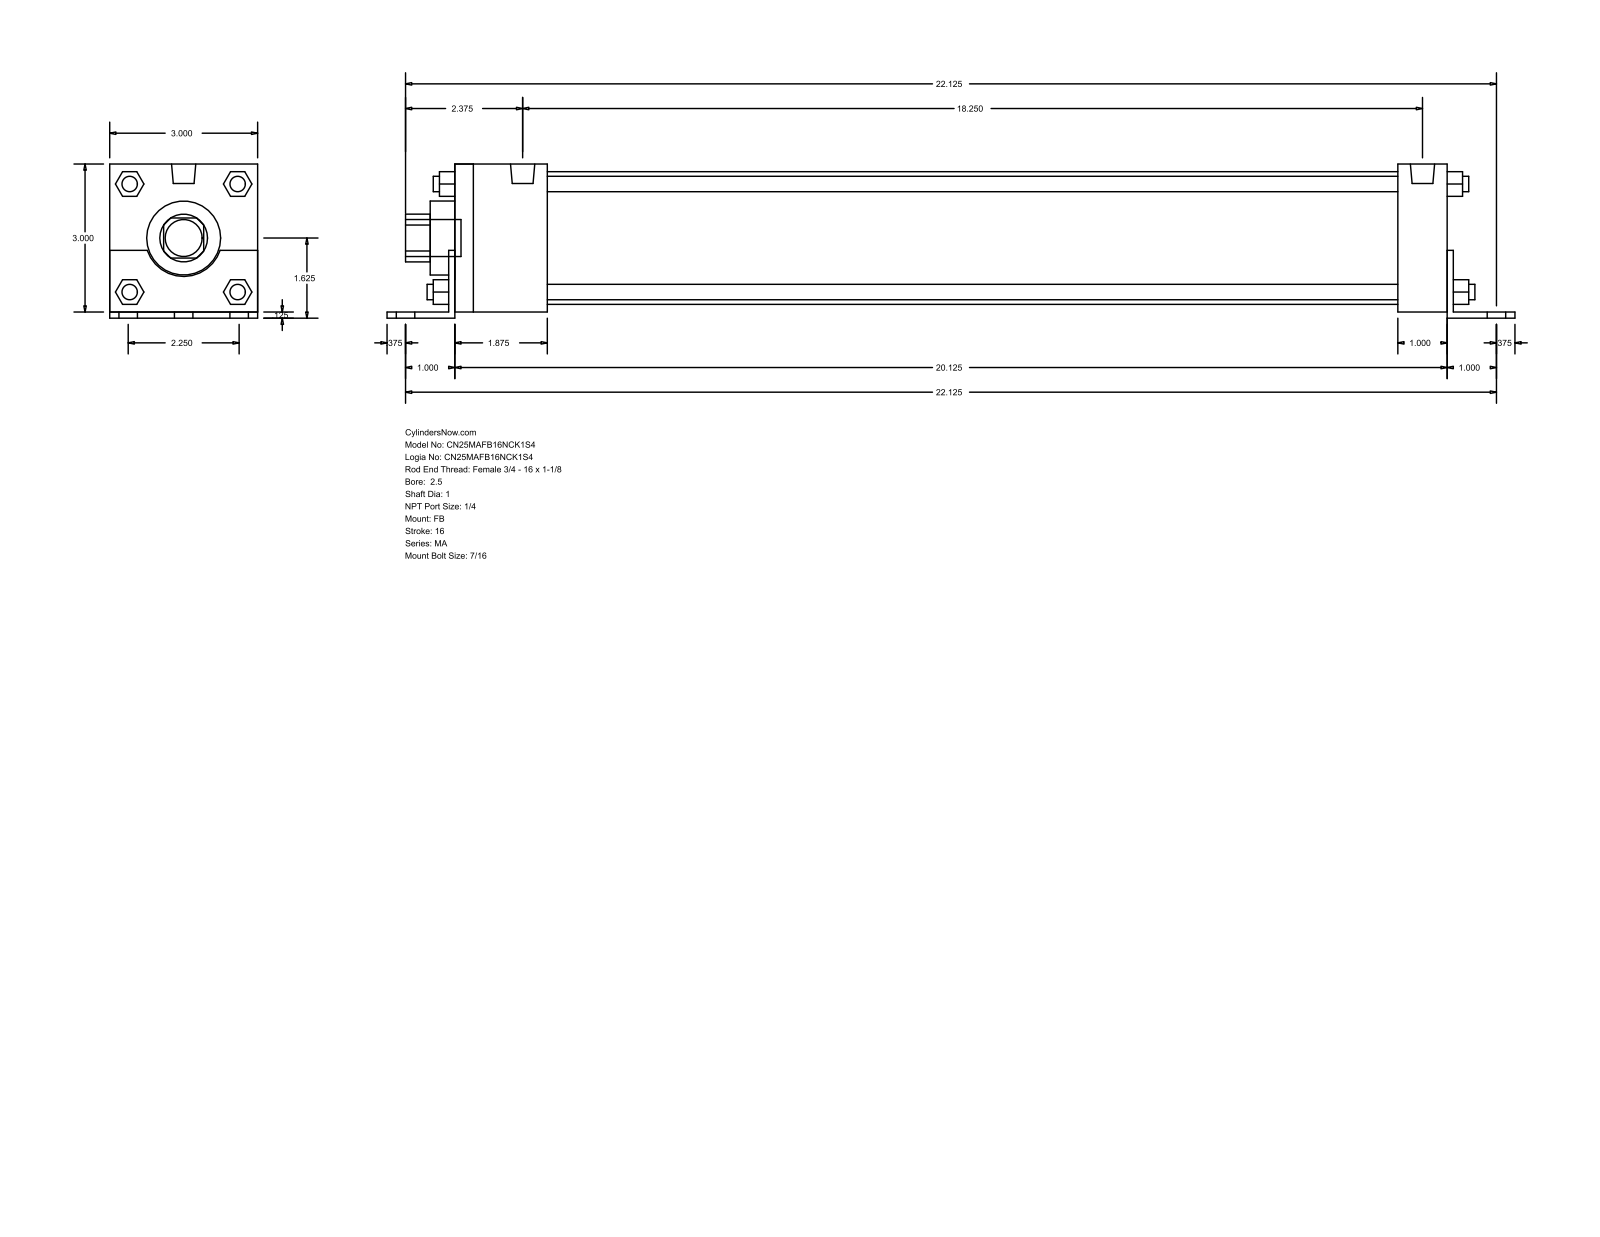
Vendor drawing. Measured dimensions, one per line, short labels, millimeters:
name: MA_FB__0250_1
written by: GSSL Pune (CONFIG_CONTROL_DESIGN)
unit: mm
bodies: 0 solids, 140 faces (105 planar, 35 cylindrical, 0 other)
size: 581.02 × 79.38 × 76.2
holes: 1× ⌀25.4, 1× ⌀38.1, 1× ⌀68.33
bosses: 8× ⌀7.94, 6× ⌀11.11, 2× ⌀12.49, 1× ⌀19.05
rounds: 1× R12.29, 1× R19.81
face distances: 76.2, 3.17, 79.37, 514.35, 511.18, 12.7, 25.4, 28.57, 47.63, 463.55
